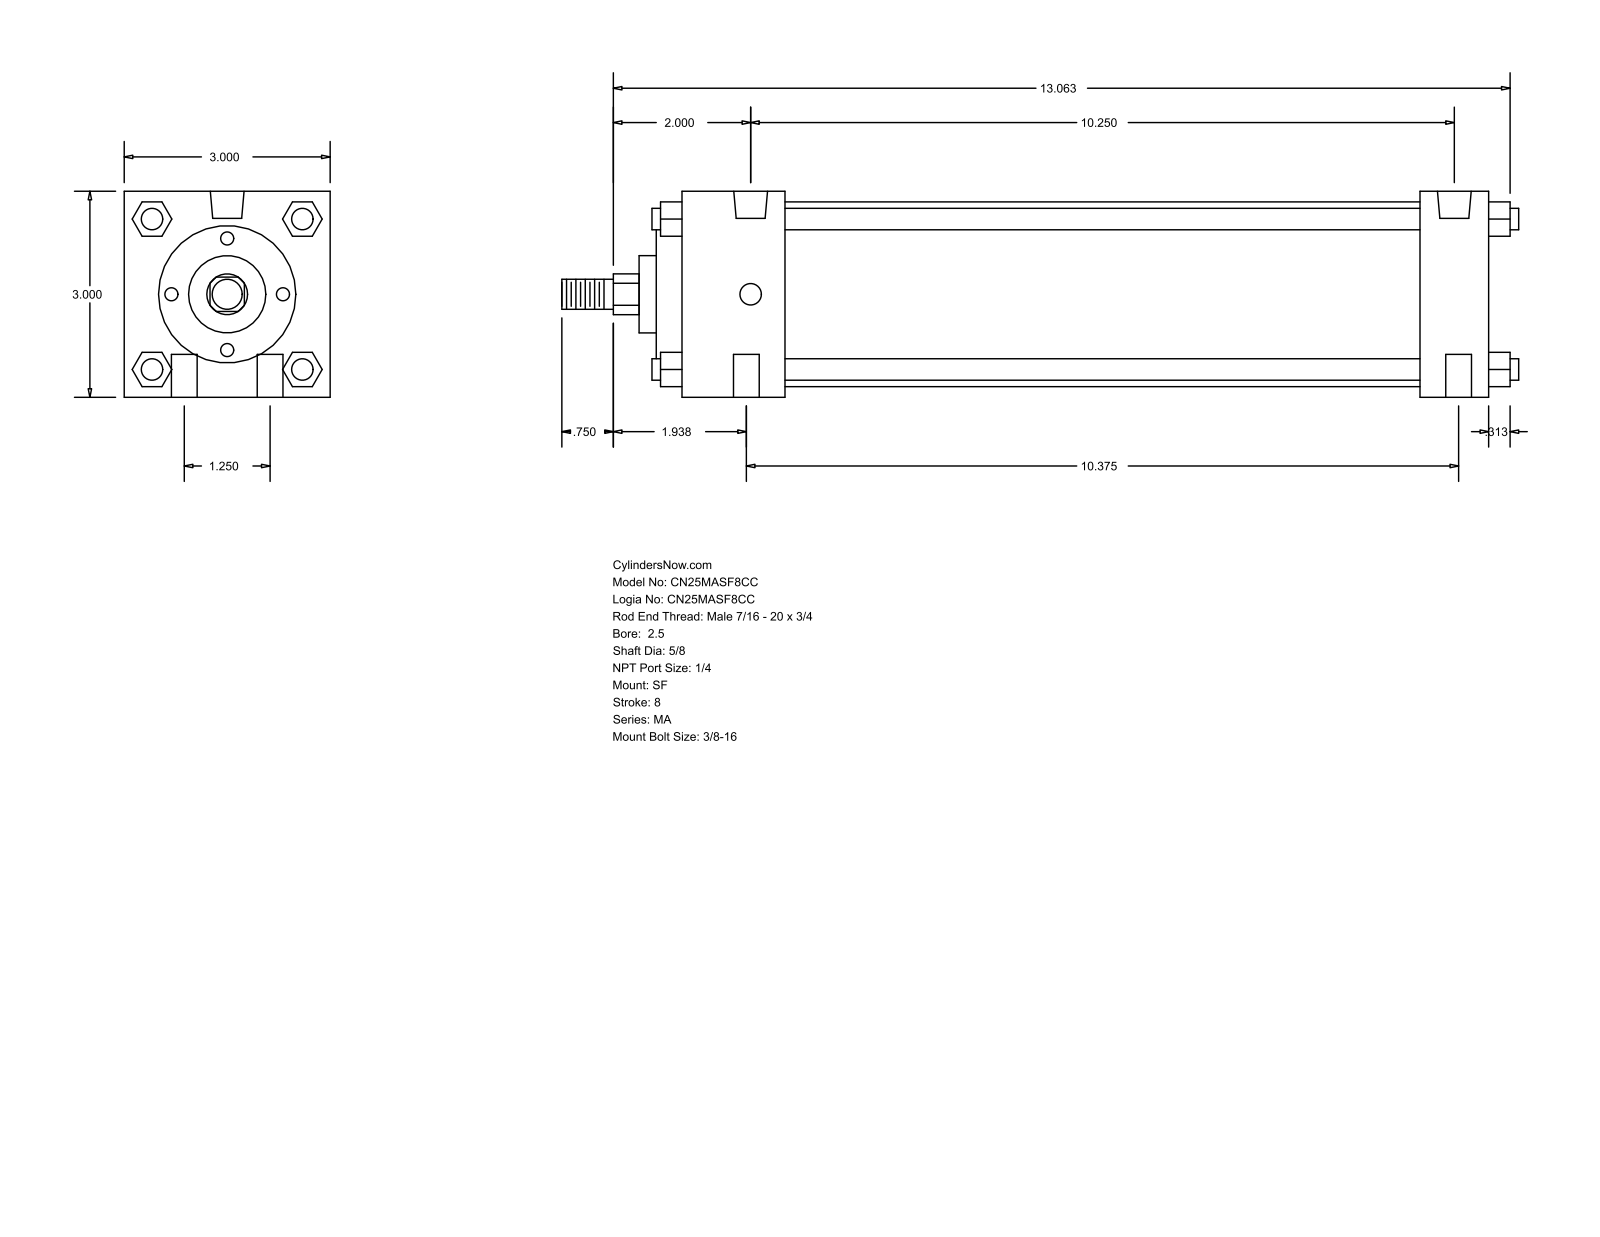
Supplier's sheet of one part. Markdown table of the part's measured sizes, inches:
| quantity | value |
| --- | --- |
| part name | MA_SF__0250_0.625 |
| STEP written by | GSSL Pune (CONFIG_CONTROL_DESIGN) |
| units | inches |
| bodies | 0 solids, 126 faces (95 planar, 31 cylindrical, 0 other) |
| overall size | 13.937 × 3 × 3 |
| round holes (diameter × count) | 0.375 × 4, 0.313 × 2, 0.492 × 2 |
| round bosses / shafts (diameter × count) | 0.313 × 4, 2.69 × 1, 2 × 1, 1.125 × 1, 0.625 × 1, 0.437 × 1 |
| partial cylindrical surfaces (radius × count) | 0.297 × 1 |
| main face-to-face distances | 3, 11.75, 1, 10.75, 1.5, 9.25, 10.25, 0.5, 0.375, 1.875 |
| hole center spacings | 0.628, 10.331, 1.25, 10.25, 10.375, 10.45 |
